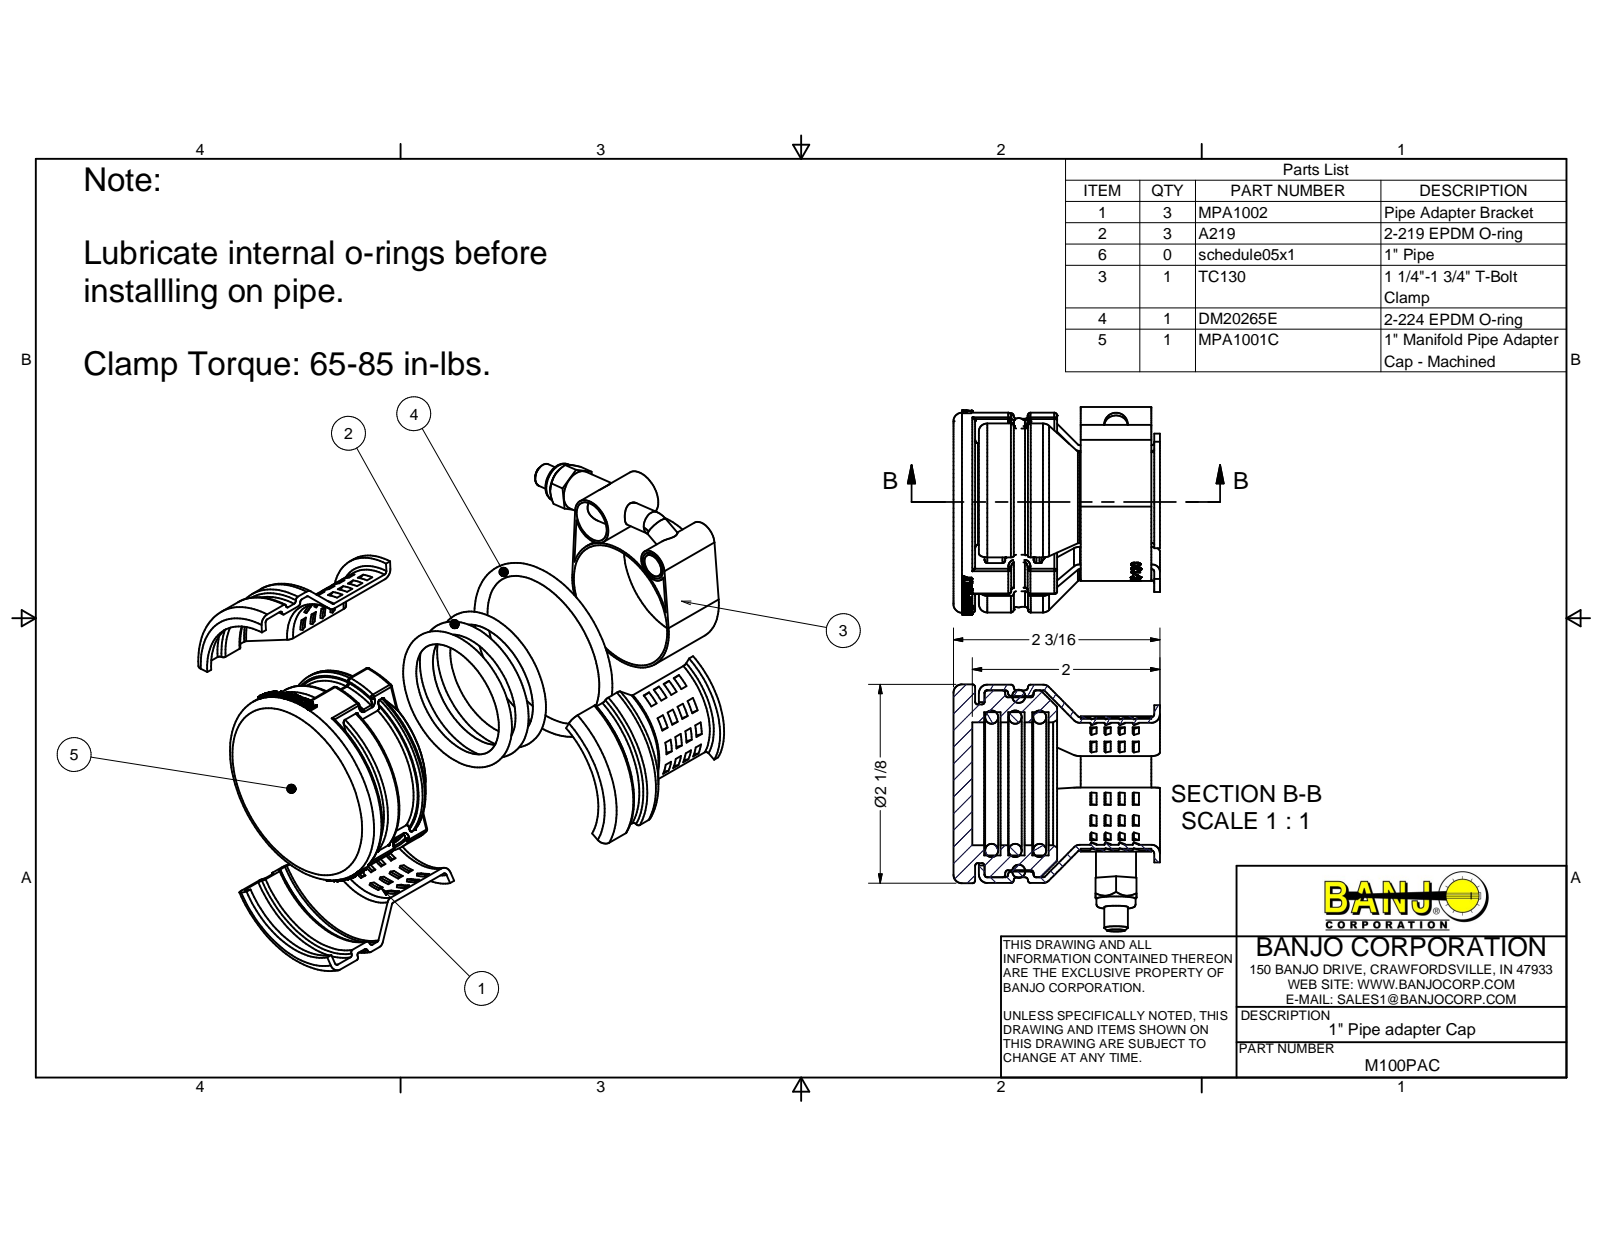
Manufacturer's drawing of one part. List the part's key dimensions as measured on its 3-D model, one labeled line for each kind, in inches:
Part name (STEP PRODUCT): M100PAC; MPA1001C; MPA1001CX; MPA1002 (+3 more)
STEP written by: Autodesk Inventor 2012 (AUTOMOTIVE_DESIGN)
Units: inches
Bodies: 9 solids, 1272 faces (522 planar, 162 cylindrical, 588 other)
Overall size (bounding box): 2.632 × 2.206 × 2.19
Volume: 3.092 in³ · Surface area: 65.55 in²
Round holes (diameter × count): ⌀0.3 ×1, ⌀0.45 ×1, ⌀1.325 ×1, ⌀1.4 ×1, ⌀1.54 ×1
Round bosses / shafts (diameter × count): ⌀2.125 ×1, ⌀1.45 ×1, ⌀0.5 ×1, ⌀0.425 ×1, ⌀0.415 ×1, ⌀0.35 ×1, ⌀0.25 ×1
Partial cylindrical surfaces — rounded edges, fillets, slot ends (radius × count): R0.03 ×30, R0.658 ×1, R0.718 ×1, R0.72 ×1, R0.843 ×1, R0.85 ×1, R0.875 ×1, R0.925 ×1
Main face-to-face distances: 0.255, 0.2, 0.23, 0.77, 0.03, 0.27, 0.08, 0.175, 0.9, 1.1
Hole centre spacings: 0.9, 0.925, 0.975
